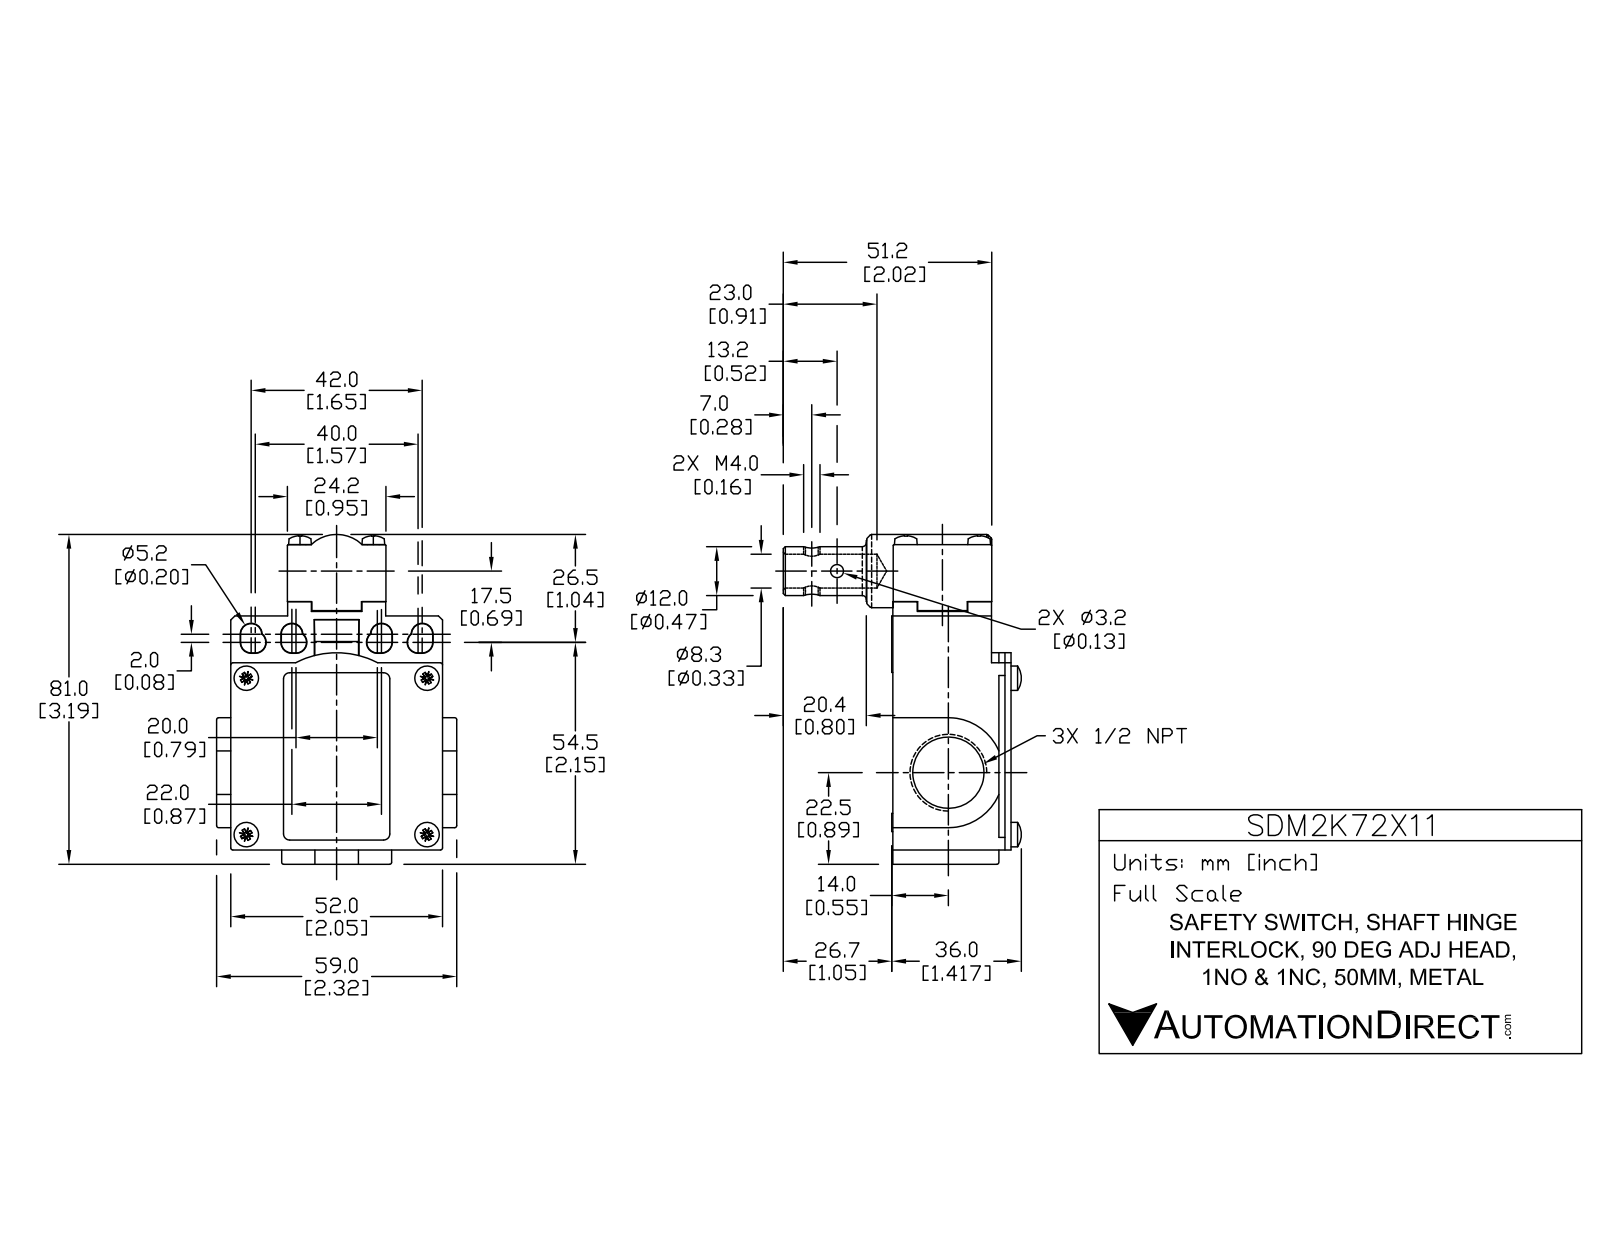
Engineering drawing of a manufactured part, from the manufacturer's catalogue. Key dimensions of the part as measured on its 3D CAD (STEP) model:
Part name (STEP PRODUCT): SDM2K72X11
STEP written by: SolidWorks 2017 (AUTOMOTIVE_DESIGN)
Units: inches
Bodies: 3 solids, 230 faces (99 planar, 93 cylindrical, 38 other)
Overall size (bounding box): 3.189 × 2.323 × 2.309
Volume: 5.904 in³ · Surface area: 33.88 in²
Round holes (diameter × count): ⌀0.669 ×2, ⌀0.748 ×2, ⌀0.126 ×1, ⌀0.157 ×1, ⌀0.327 ×1, ⌀0.465 ×1, ⌀0.587 ×1
Round bosses / shafts (diameter × count): ⌀0.22 ×4, ⌀0.217 ×4, ⌀0.709 ×1, ⌀0.472 ×1
Partial cylindrical surfaces — rounded edges, fillets, slot ends (radius × count): R0.02 ×14, R0.102 ×12, R0.531 ×2, R0.394 ×1, R0.4 ×1, R0.866 ×1
Main face-to-face distances: 1.144, 0.138, 0.945, 2.047, 0.551, 0.689, 0.199, 2.307, 0.236, 1.496
Hole centre spacings: 1.089, 2.361
